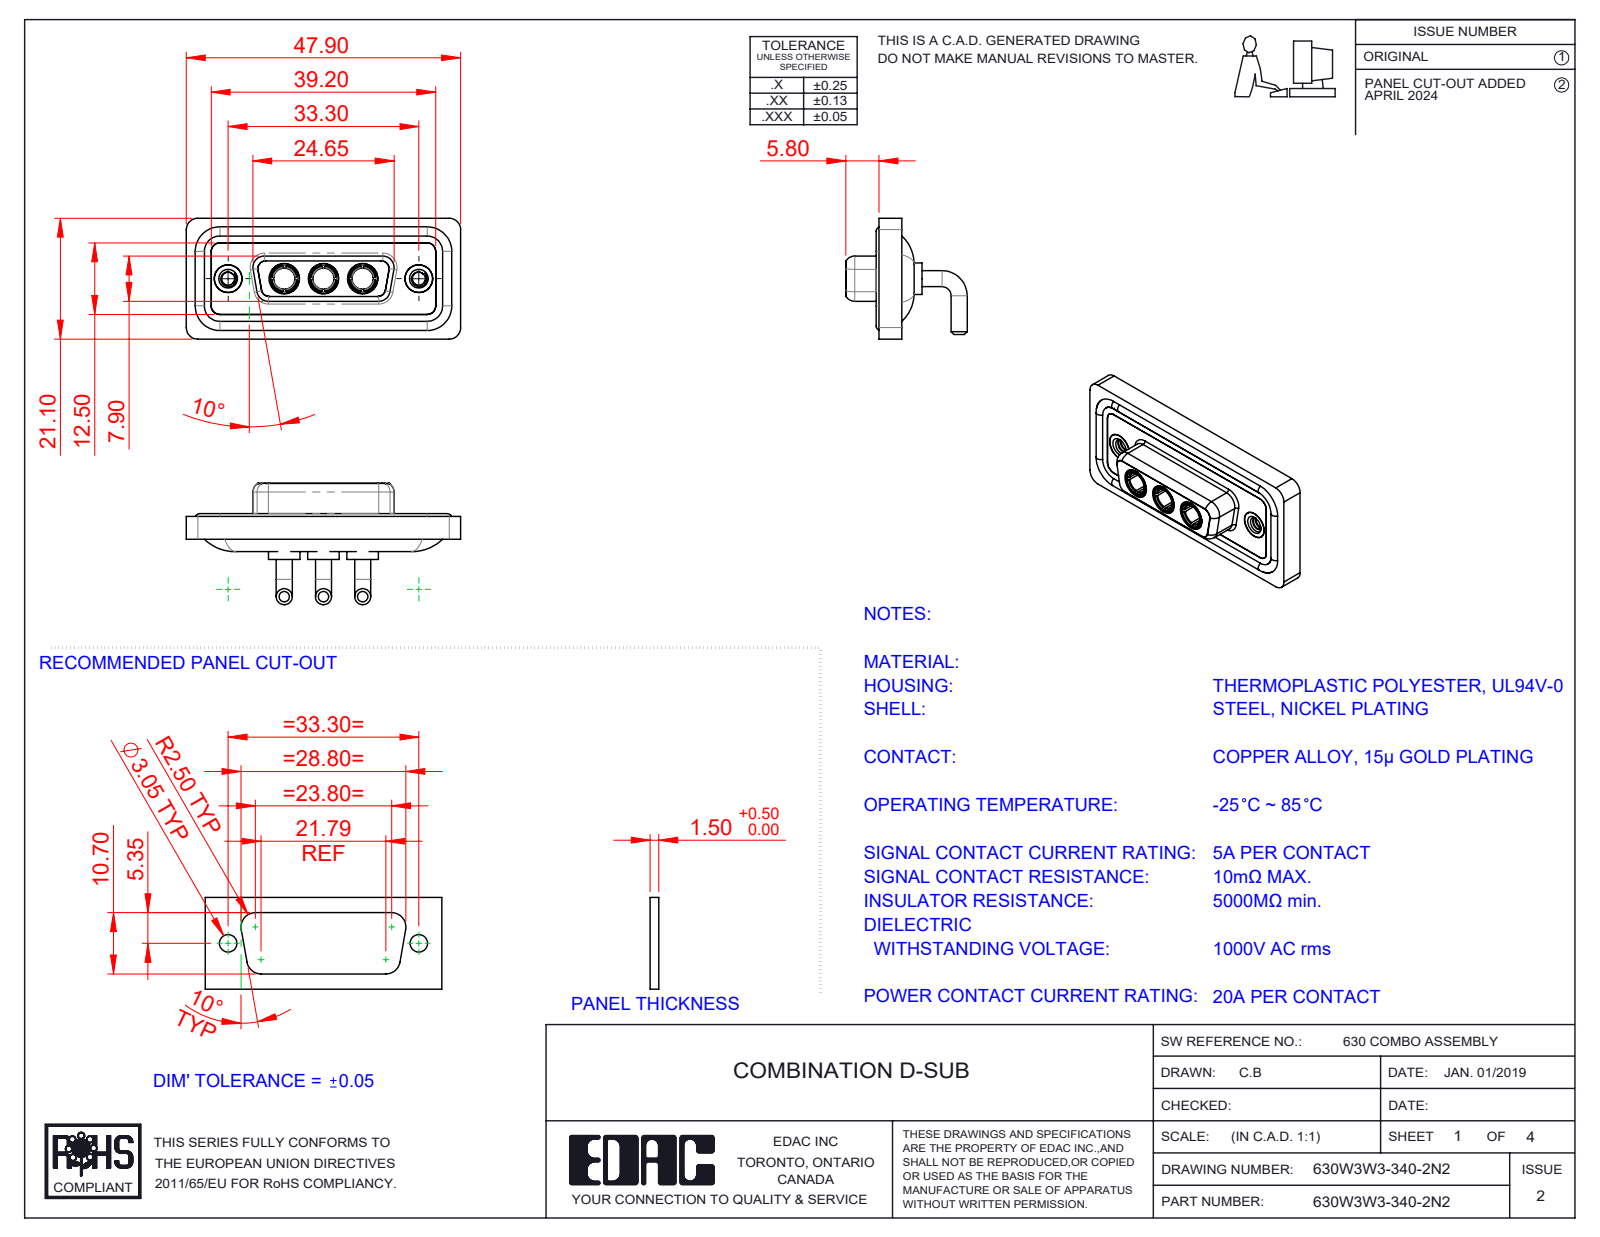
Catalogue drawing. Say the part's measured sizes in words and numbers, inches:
The part is named "Power Socket_20A RA; 630Combo Waterproof Housing_15 Contacts; 630Combo Shell Rear_15 Contacts; 630W3W3-340-2N2 (+3 more)". Its 3-D file was written by "SolidWorks 2023 (CONFIG_CONTROL_DESIGN)". It is 13 solids with 620 faces: 192 planar, 263 cylindrical and 165 other. Overall it measures 1.886 by 0.835 by 0.831 inches. Its volume is 0.377 cubic inches and its surface area 15.46 square inches. Round holes: 5 of diameter 0.191, 3 of diameter 0.146, 3 of diameter 0.209, 2 of diameter 0.089, 2 of diameter 0.157, 2 of diameter 0.159, 2 of diameter 0.197. Round bosses or shafts: 6 of diameter 0.11, 4 of diameter 0.063, 3 of diameter 0.217, 3 of diameter 0.205, 3 of diameter 0.195, 3 of diameter 0.187, 3 of diameter 0.148, 2 of diameter 0.195. Partial cylindrical surfaces (rounded edges, fillets, slot ends): 20 of radius 0.079, 18 of radius 0.059, 12 of radius 0.053, 8 of radius 0.063, 4 of radius 0.01, 4 of radius 0.02, 4 of radius 0.024, 4 of radius 0.026. The main face-to-face distances are 0.016, 0.071, 0.043, 0.063, 0.114, 0.098, 0.122, 0.146, 0.161, 0.059. The hole center spacings are 0.27, 0.386, 0.656, 0.925, 0.539, 1.311.
